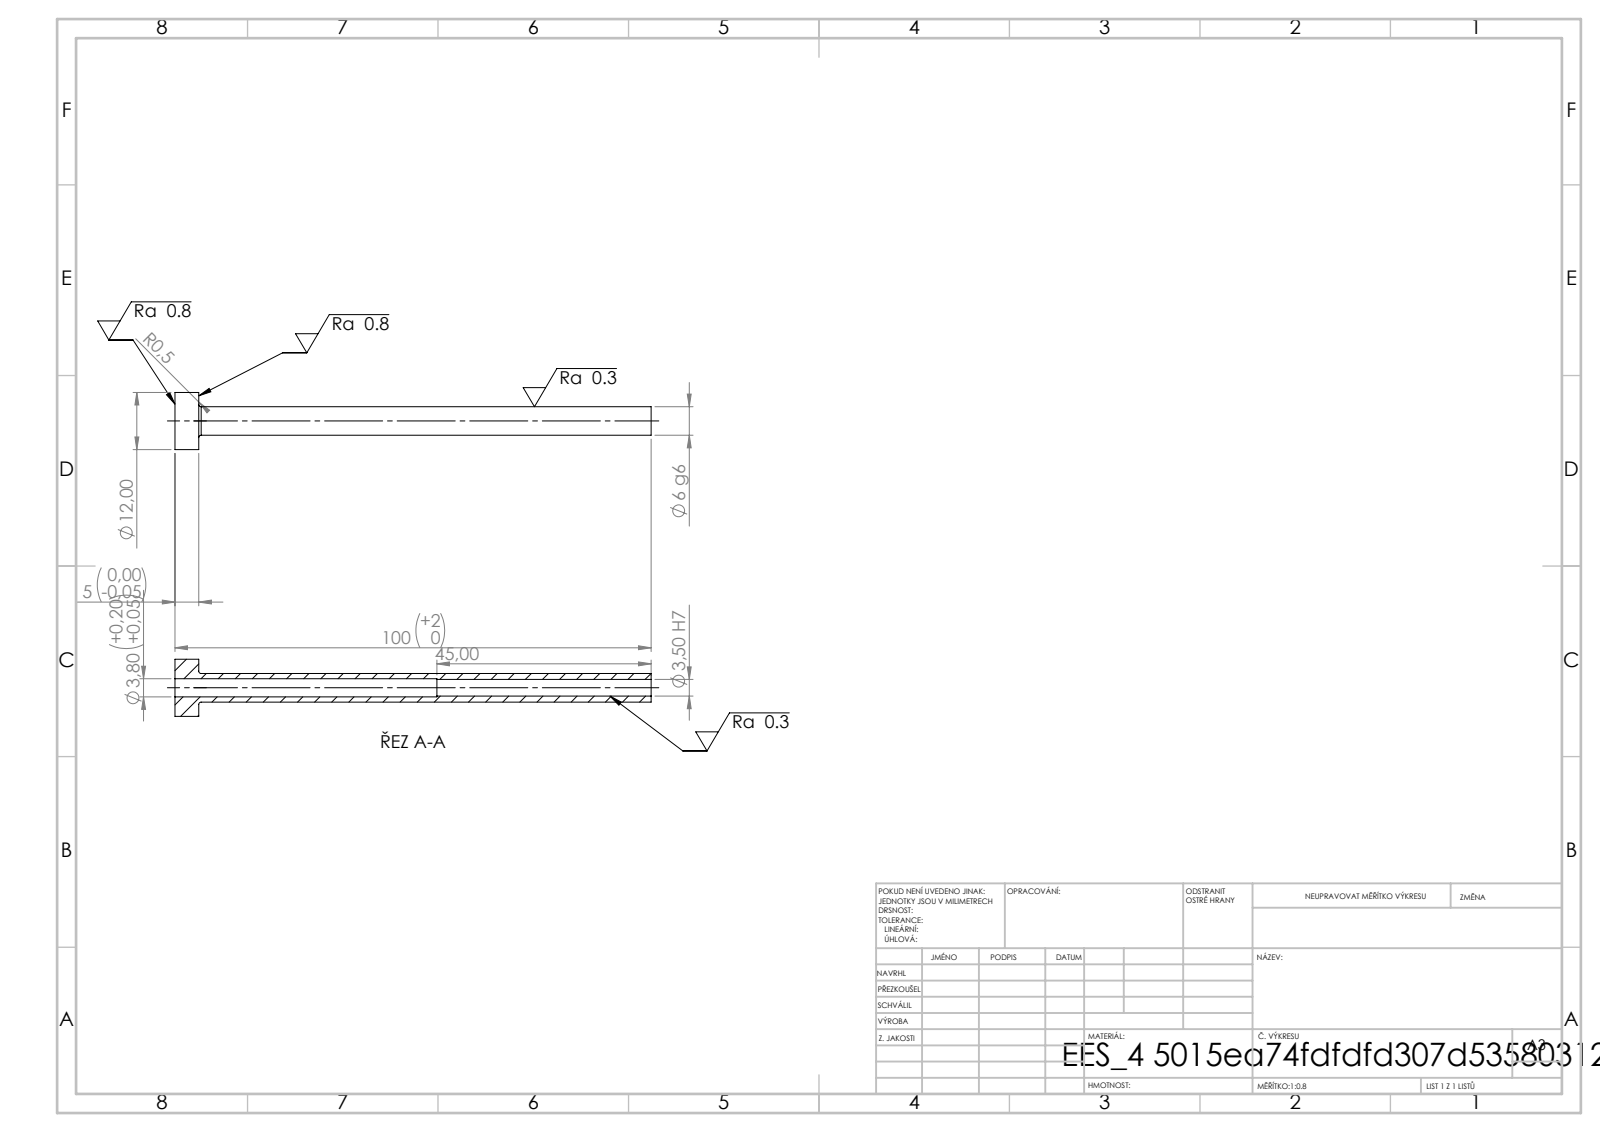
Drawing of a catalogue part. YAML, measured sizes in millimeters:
step_written_by: "SolidWorks 2019 (CONFIG_CONTROL_DESIGN)"
units: millimeters
bodies: {solids: 1, faces: 14, planar: 4, cylindrical: 8, other: 2}
overall_size: [100, 12, 12]
volume: 2196
surface_area: 3334
round_holes:
  - {diameter: 3.5, count: 1}
  - {diameter: 3.8, count: 1}
round_bosses_or_shafts:
  - {diameter: 12, count: 1}
  - {diameter: 6, count: 1}
face_to_face_distances: [5, 100, 95, 55, 50, 45]
